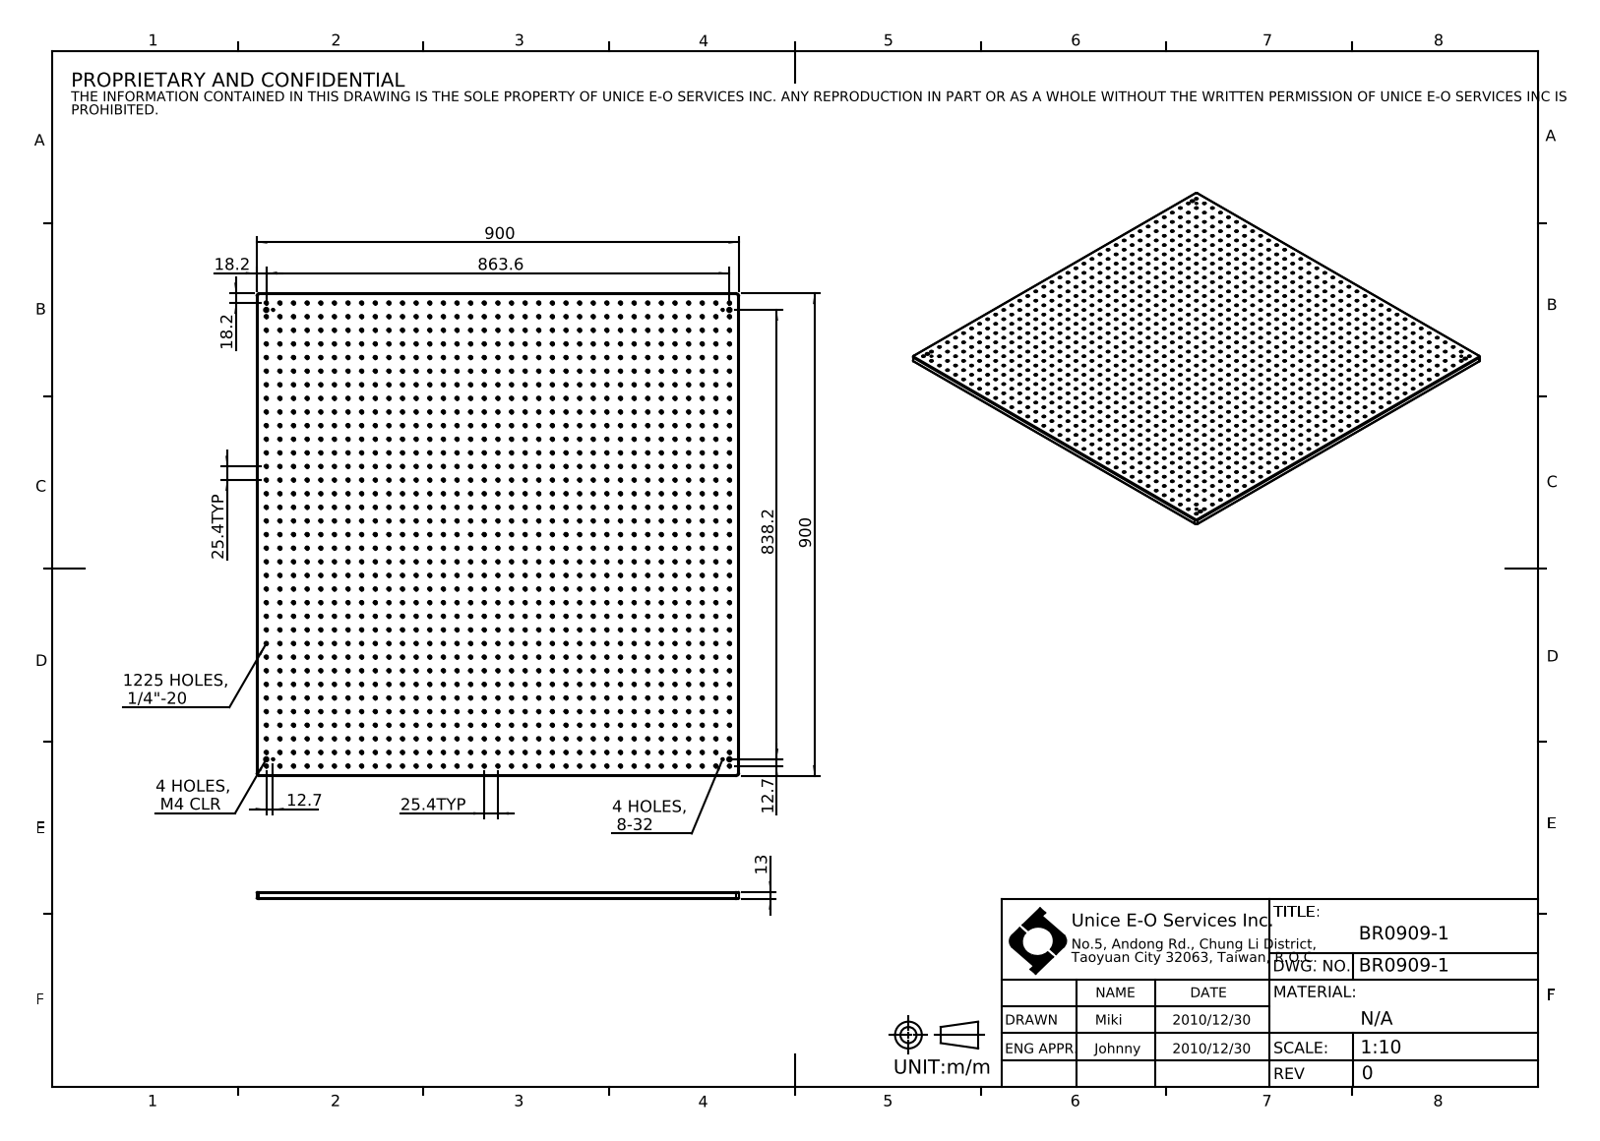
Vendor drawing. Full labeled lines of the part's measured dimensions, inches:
Part name (STEP PRODUCT): BR0909-1
STEP written by: SolidWorks 2016 (CONFIG_CONTROL_DESIGN)
Units: inches
Bodies: 1 solid, 2504 faces (10 planar, 2486 cylindrical, 8 other)
Overall size (bounding box): 35.433 × 35.433 × 0.512
Volume: 622.4 in³ · Surface area: 2 894 in²
Round holes (diameter × count): ⌀0.201 ×1225, ⌀0.136 ×4, ⌀0.177 ×4, ⌀0.315 ×4
Partial cylindrical surfaces — rounded edges, fillets, slot ends (radius × count): R0.079 ×8, R0.197 ×4
Main face-to-face distances: 0.512, 35.433, 0.276, 0.236
Hole centre spacings: 1, 2, 3, 4, 5, 6, 7, 8
